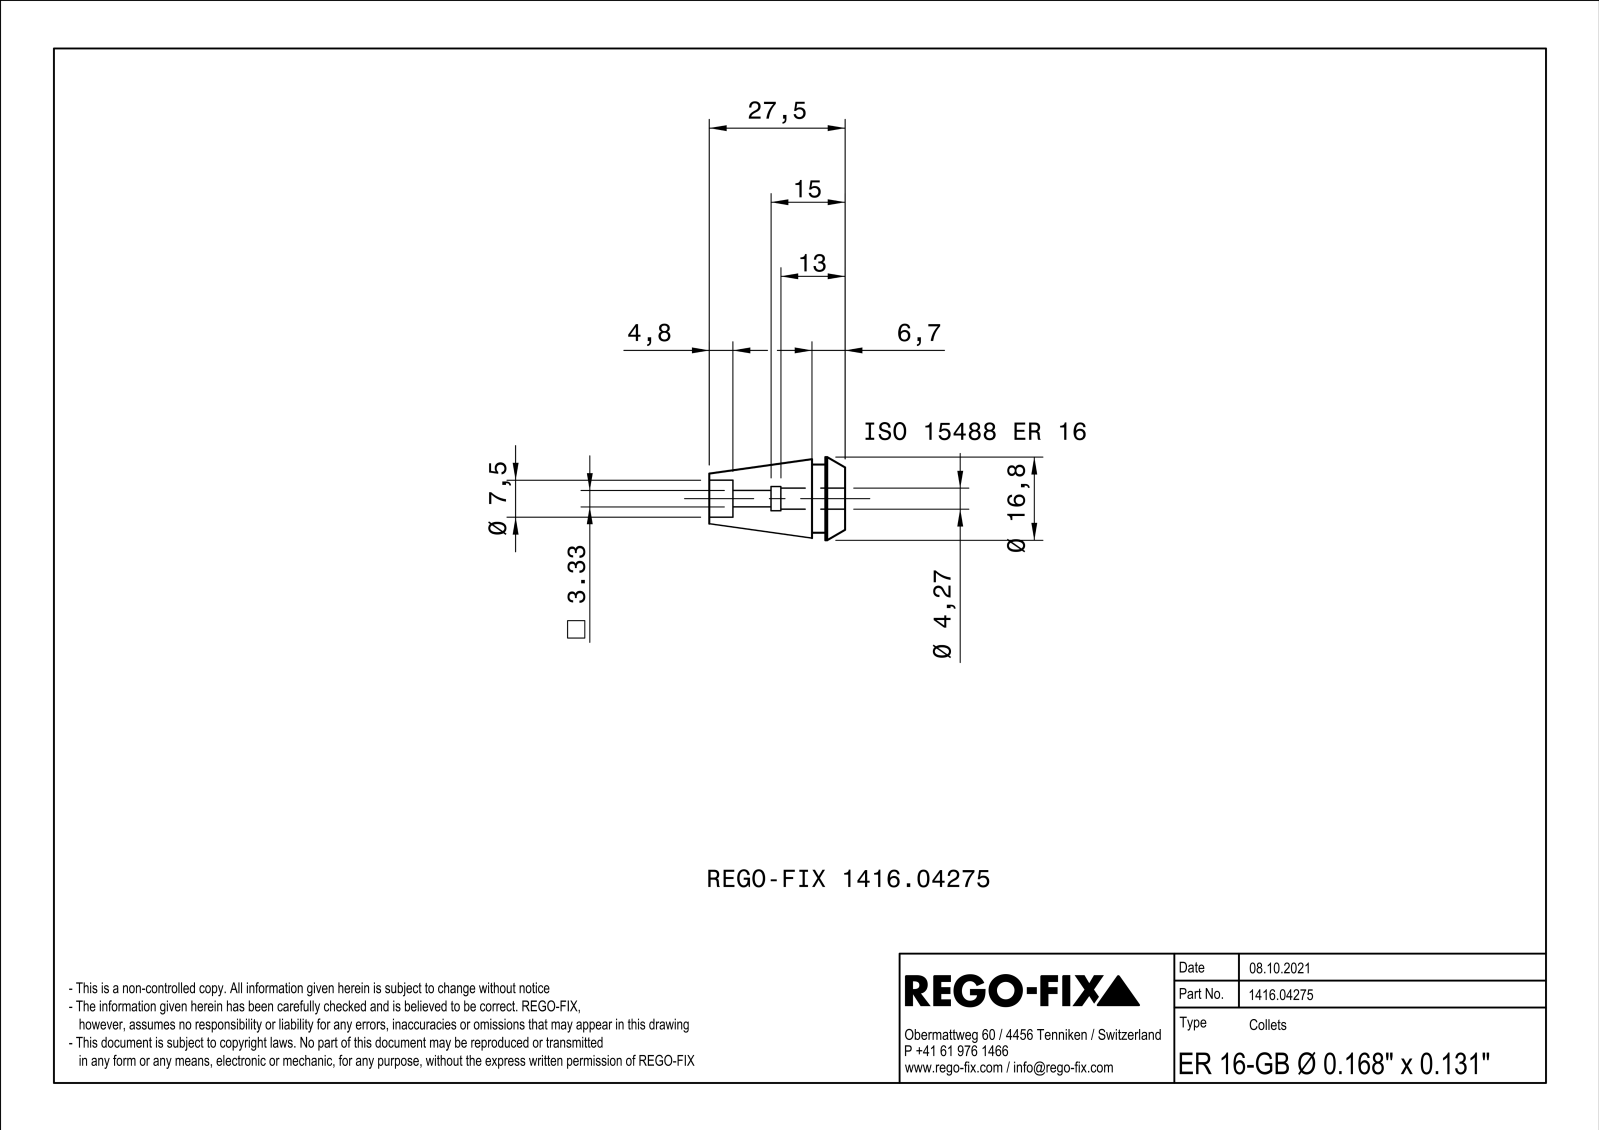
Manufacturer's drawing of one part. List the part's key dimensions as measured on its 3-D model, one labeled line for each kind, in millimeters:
Part name (STEP PRODUCT): NOCUT
STEP written by: SIEMENS PLM Software Solid Edge ST10 (AUTOMOTIVE_DESIGN)
Units: millimetres
Bodies: 1 solid, 164 faces (72 planar, 32 cylindrical, 60 other)
Overall size (bounding box): 27.5 × 16.8 × 16.8
Volume: 2 911 mm³ · Surface area: 3 326 mm²
Round holes (diameter × count): ⌀4.27 ×1, ⌀7.5 ×1
Round bosses / shafts (diameter × count): ⌀16.8 ×1, ⌀13.8 ×1
Partial cylindrical surfaces — rounded edges, fillets, slot ends (radius × count): R1.9 ×1, R2.45 ×1
Main face-to-face distances: 0.6, 4, 1.5, 2.1, 6.7, 2.7, 3.6, 27.5, 23.5, 20.8
